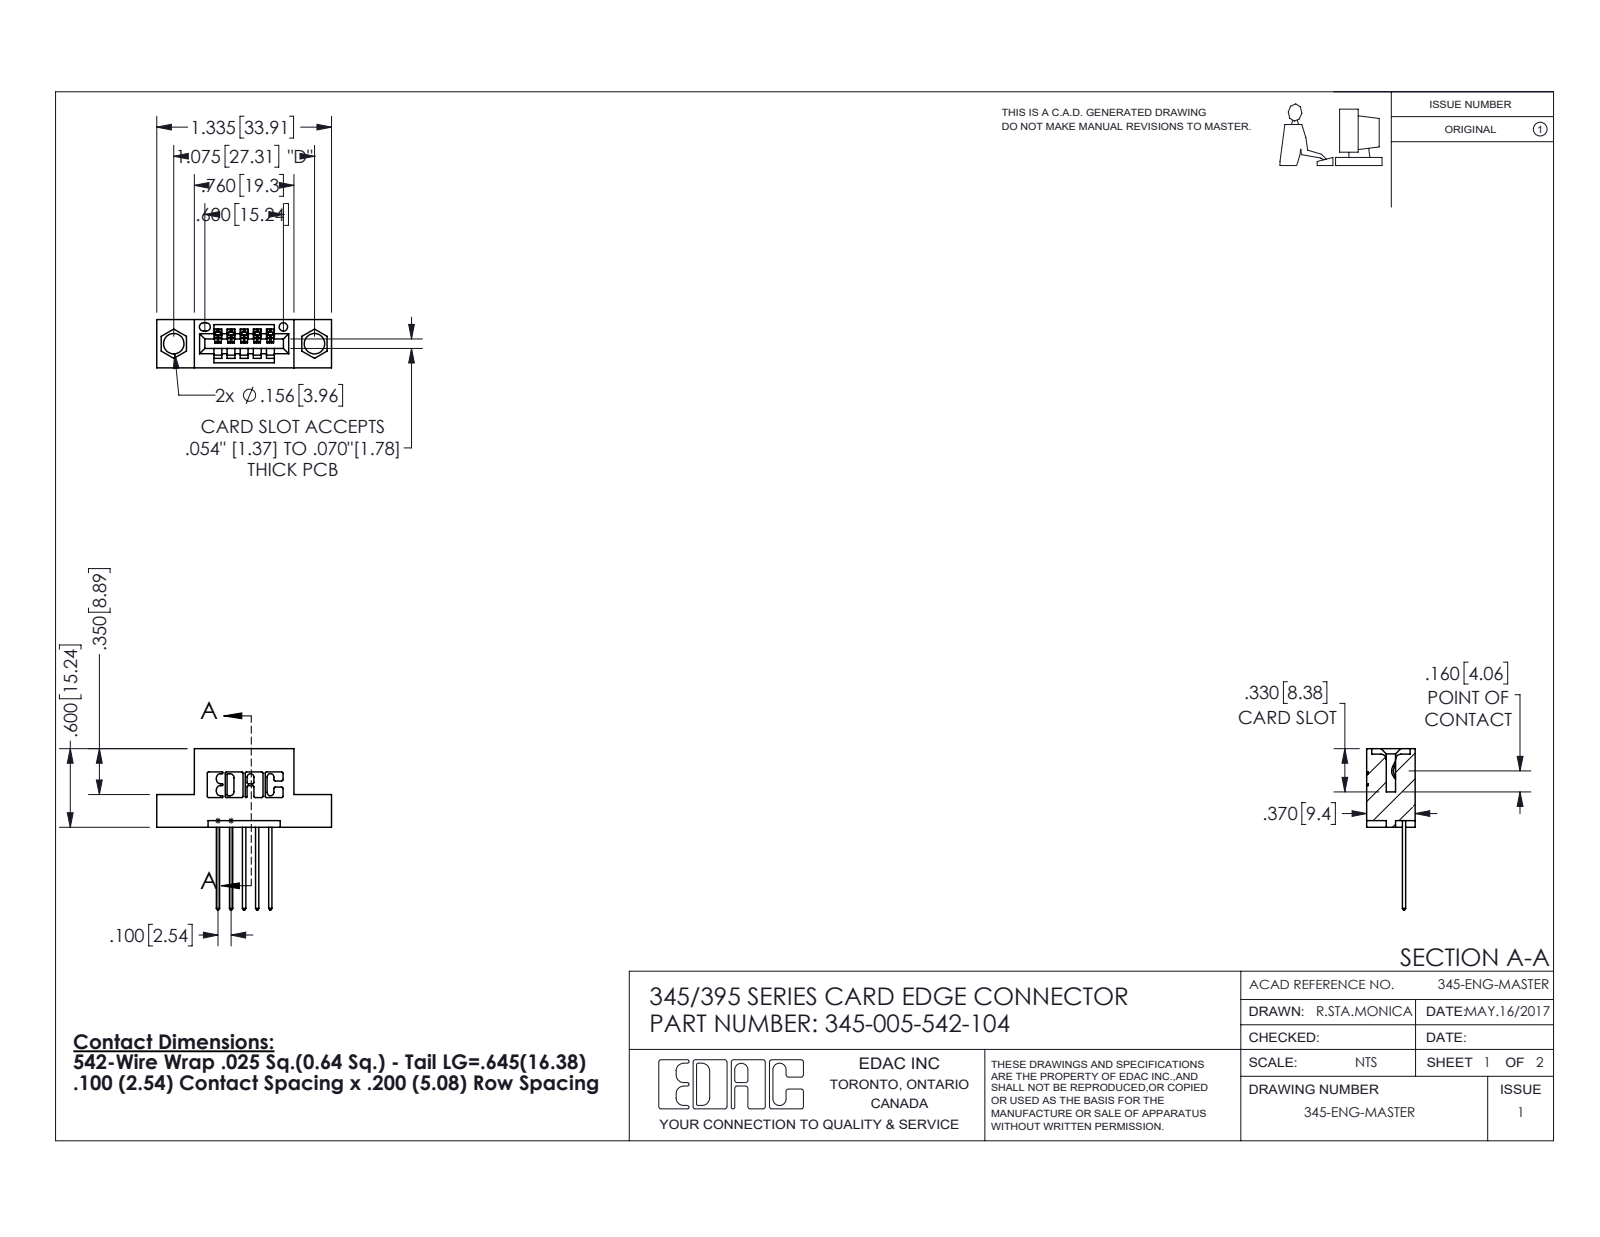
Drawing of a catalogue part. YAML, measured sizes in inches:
part_name: "345 Part_Flush Mounting Lugs - 0.156 Dia-TI; 345-292-001_345-293-142; 345-005-542-104"
step_written_by: "SolidWorks 2020 (CONFIG_CONTROL_DESIGN)"
units: inches
bodies: {solids: 6, faces: 430, planar: 294, cylindrical: 136, other: 0}
overall_size: [1.335, 1.232, 0.37]
volume: 0.172
surface_area: 4.9
round_holes:
  - {diameter: 0.156, count: 2}
  - {diameter: 0.064, count: 1}
partial_cylinders:
  - {radius: 0.01, count: 22}
  - {radius: 0.006, count: 10}
  - {radius: 0.01, count: 10}
  - {radius: 0.007, count: 6}
  - {radius: 0.031, count: 6}
  - {radius: 0.026, count: 3}
  - {radius: 0.031, count: 2}
  - {radius: 0.04, count: 2}
face_to_face_distances: [0.2, 0.37, 0.072, 0.298, 0.1, 0.098, 0.272, 0.025, 0.25, 0.06]
hole_center_spacings: [0.27, 0.847, 1.075]
